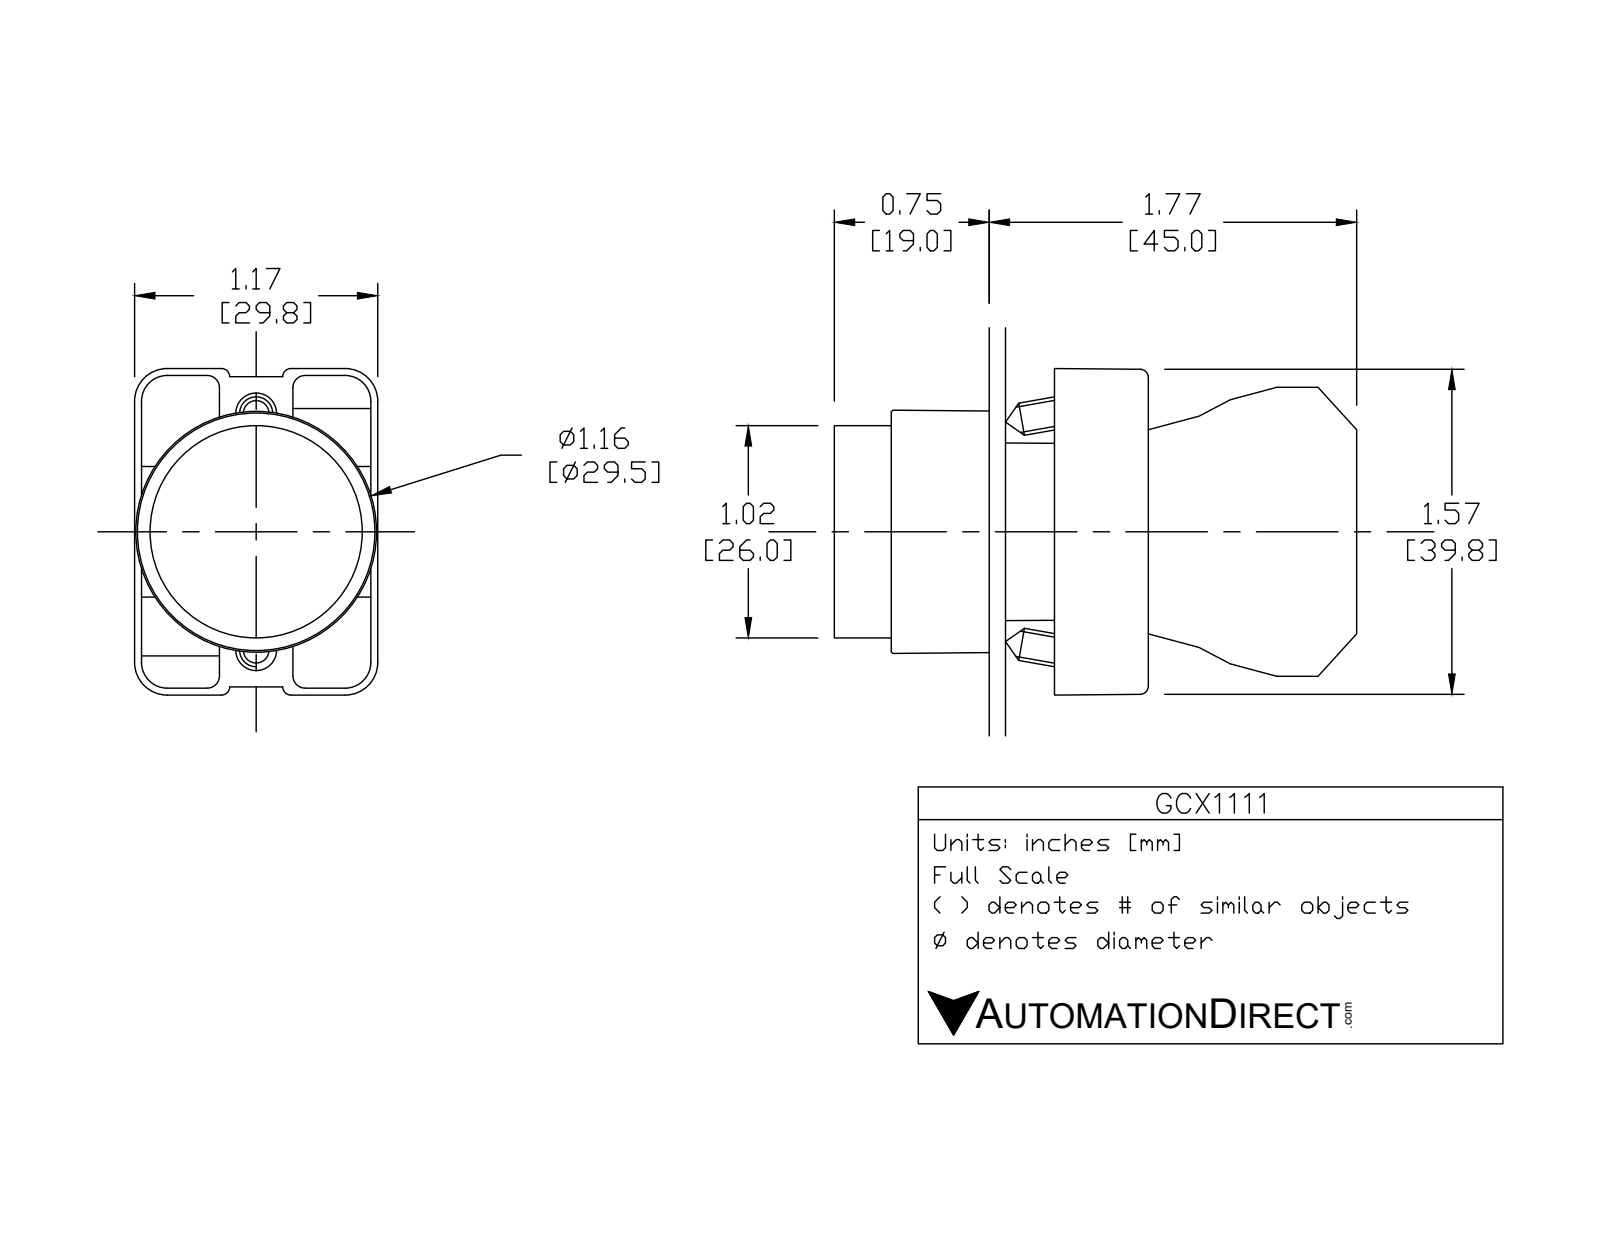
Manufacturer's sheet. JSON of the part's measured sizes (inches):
{"part_name": "ecx1030; ecx1029; GCX1111; GCX1111 OPERATOR", "step_written_by": "SolidWorks 2016 (AUTOMOTIVE_DESIGN)", "units": "inches", "bodies": {"solids": 6, "faces": 383, "planar": 222, "cylindrical": 132, "other": 29}, "overall_size": [2.492, 1.581, 1.177], "volume_in3": 1.584, "surface_area_in2": 26.47, "round_holes": [[0.079, 2], [0.124, 2], [0.13, 2], [0.087, 1], [0.197, 1], [0.878, 1], [0.888, 1], [1.024, 1]], "round_bosses_or_shafts": [[0.157, 2], [1.175, 1], [1.004, 1], [0.945, 1], [0.856, 1], [0.78, 1]], "partial_cylinders_radius": [[0.059, 24], [0.041, 12], [0.124, 12], [0.157, 12], [0.039, 4], [0.128, 2], [0.02, 1], [0.063, 1]], "face_to_face_distances": [0.579, 0.033, 1.193, 0.031, 0.472, 0.72, 0.276, 0.689, 0.598, 1.161], "hole_center_spacings": [0.236, 0.544, 0.472, 0.49]}
